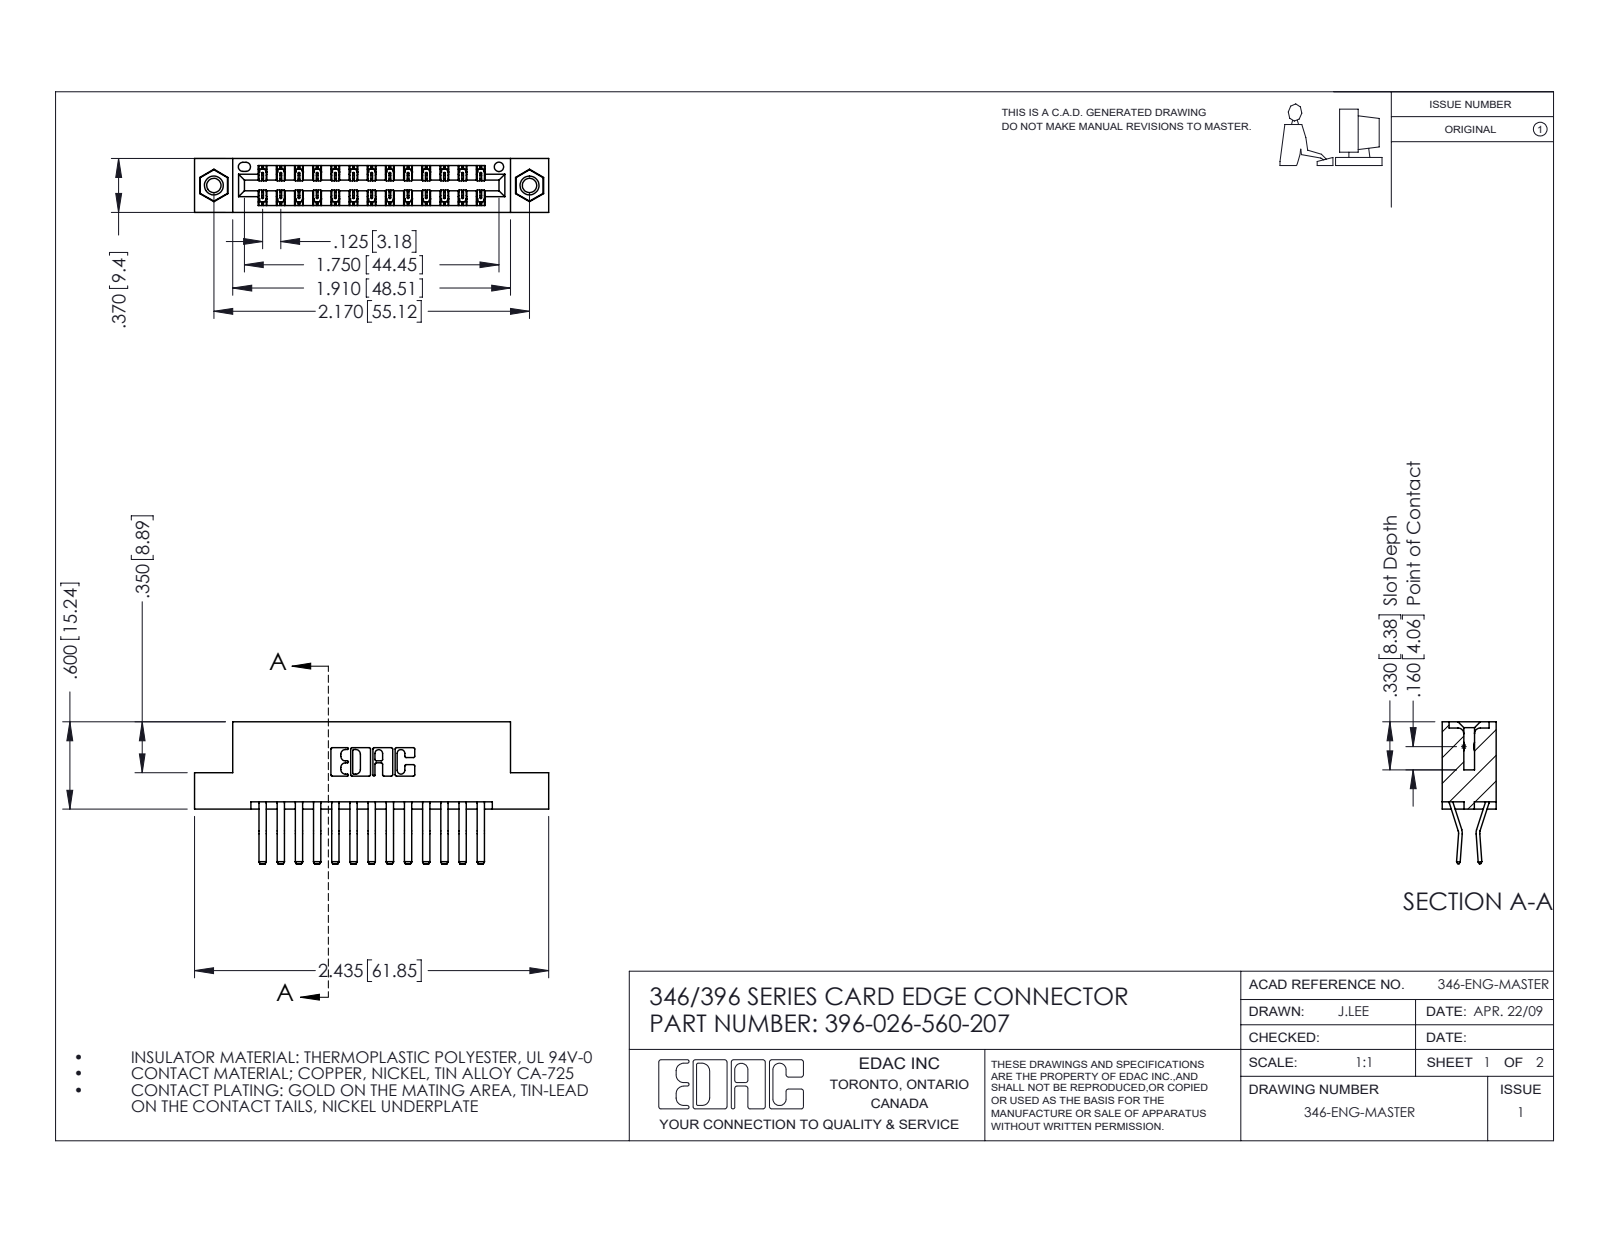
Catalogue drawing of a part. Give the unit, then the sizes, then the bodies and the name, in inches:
Units: inches
Overall size (bounding box): 2.435 × 0.975 × 0.37
Round holes (diameter × count): ⌀0.098 ×2, ⌀0.125 ×2, ⌀0.156 ×2, ⌀0.064 ×1
Round bosses / shafts (diameter × count): ⌀0.155 ×2
Partial cylindrical surfaces — rounded edges, fillets, slot ends (radius × count): R0.006 ×39, R0.01 ×22, R0.007 ×6, R0.031 ×6, R0.026 ×3, R0.01 ×2, R0.014 ×2, R0.022 ×2
Main face-to-face distances: 0.25, 0.048, 0.322, 0.37, 0.025, 0.072, 0.298, 0.275, 0.148, 0.222
Hole centre spacings: 0.246, 1.964, 2.17
Volume: 0.364 in³ · Surface area: 12.75 in²
Bodies: 29 solids, 1586 faces (1018 planar, 552 cylindrical, 16 other)
Part name (STEP PRODUCT): 346 Part_Flush Mounting Lugs - 0.156 Dia-TI; 345-292-001_560 Tail; 345-250-001_345-250-005-103; 396-026-560-207
STEP written by: SolidWorks 2016 (CONFIG_CONTROL_DESIGN)
